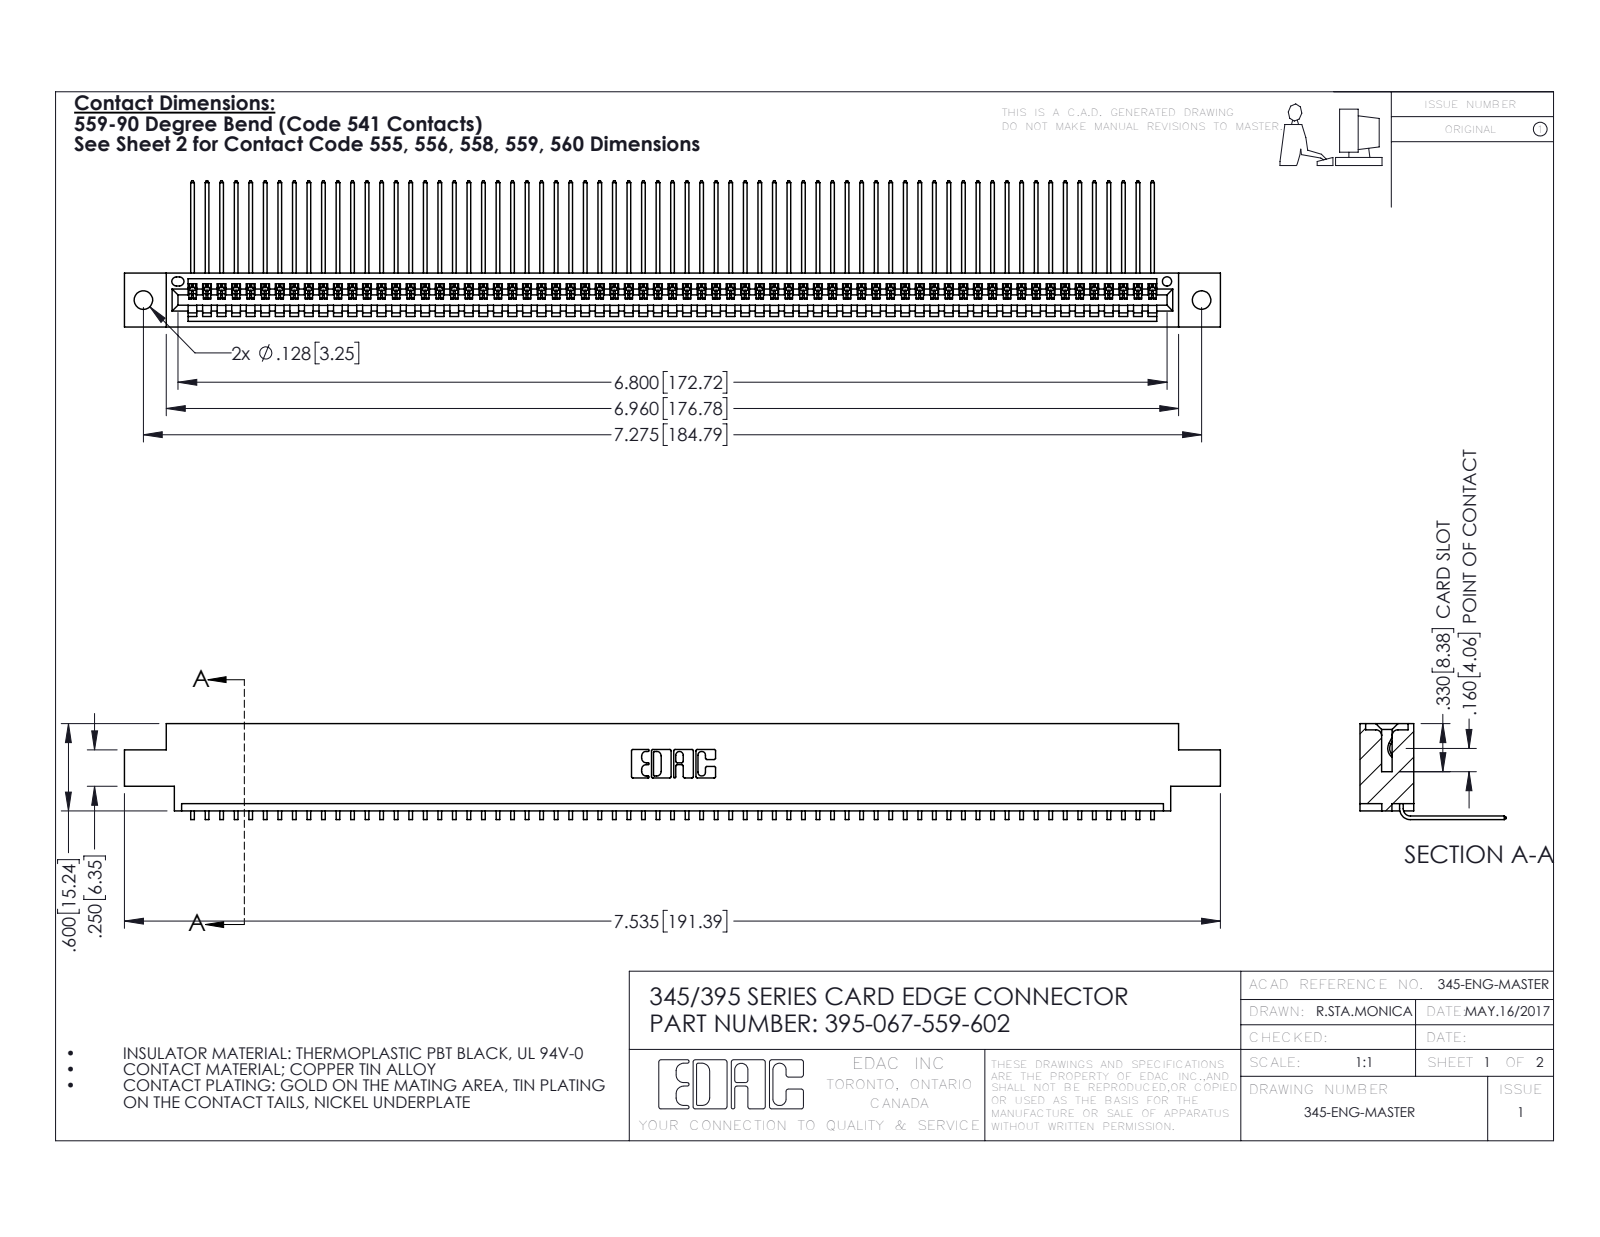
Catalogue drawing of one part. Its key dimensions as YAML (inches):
part_name: "395-067-559-602; 345 Part_0.170 Offset - 0.128 Dia; 345-292-001_558 559 Tail - 1"
step_written_by: "SolidWorks 2016 (CONFIG_CONTROL_DESIGN)"
units: inches
bodies: {solids: 68, faces: 4150, planar: 2898, cylindrical: 1252, other: 0}
overall_size: [7.535, 1.005, 0.659]
volume: 1.126
surface_area: 40.35
round_holes:
  - {diameter: 0.128, count: 2}
  - {diameter: 0.064, count: 1}
partial_cylinders:
  - {radius: 0.006, count: 134}
  - {radius: 0.01, count: 22}
  - {radius: 0.007, count: 6}
  - {radius: 0.031, count: 6}
  - {radius: 0.026, count: 3}
  - {radius: 0.031, count: 2}
  - {radius: 0.04, count: 2}
  - {radius: 0.014, count: 1}
face_to_face_distances: [0.072, 0.298, 0.37, 0.2, 0.098, 0.272, 0.025, 0.225, 0.175, 0.149]
hole_center_spacings: [0.27, 7.039, 7.275]
